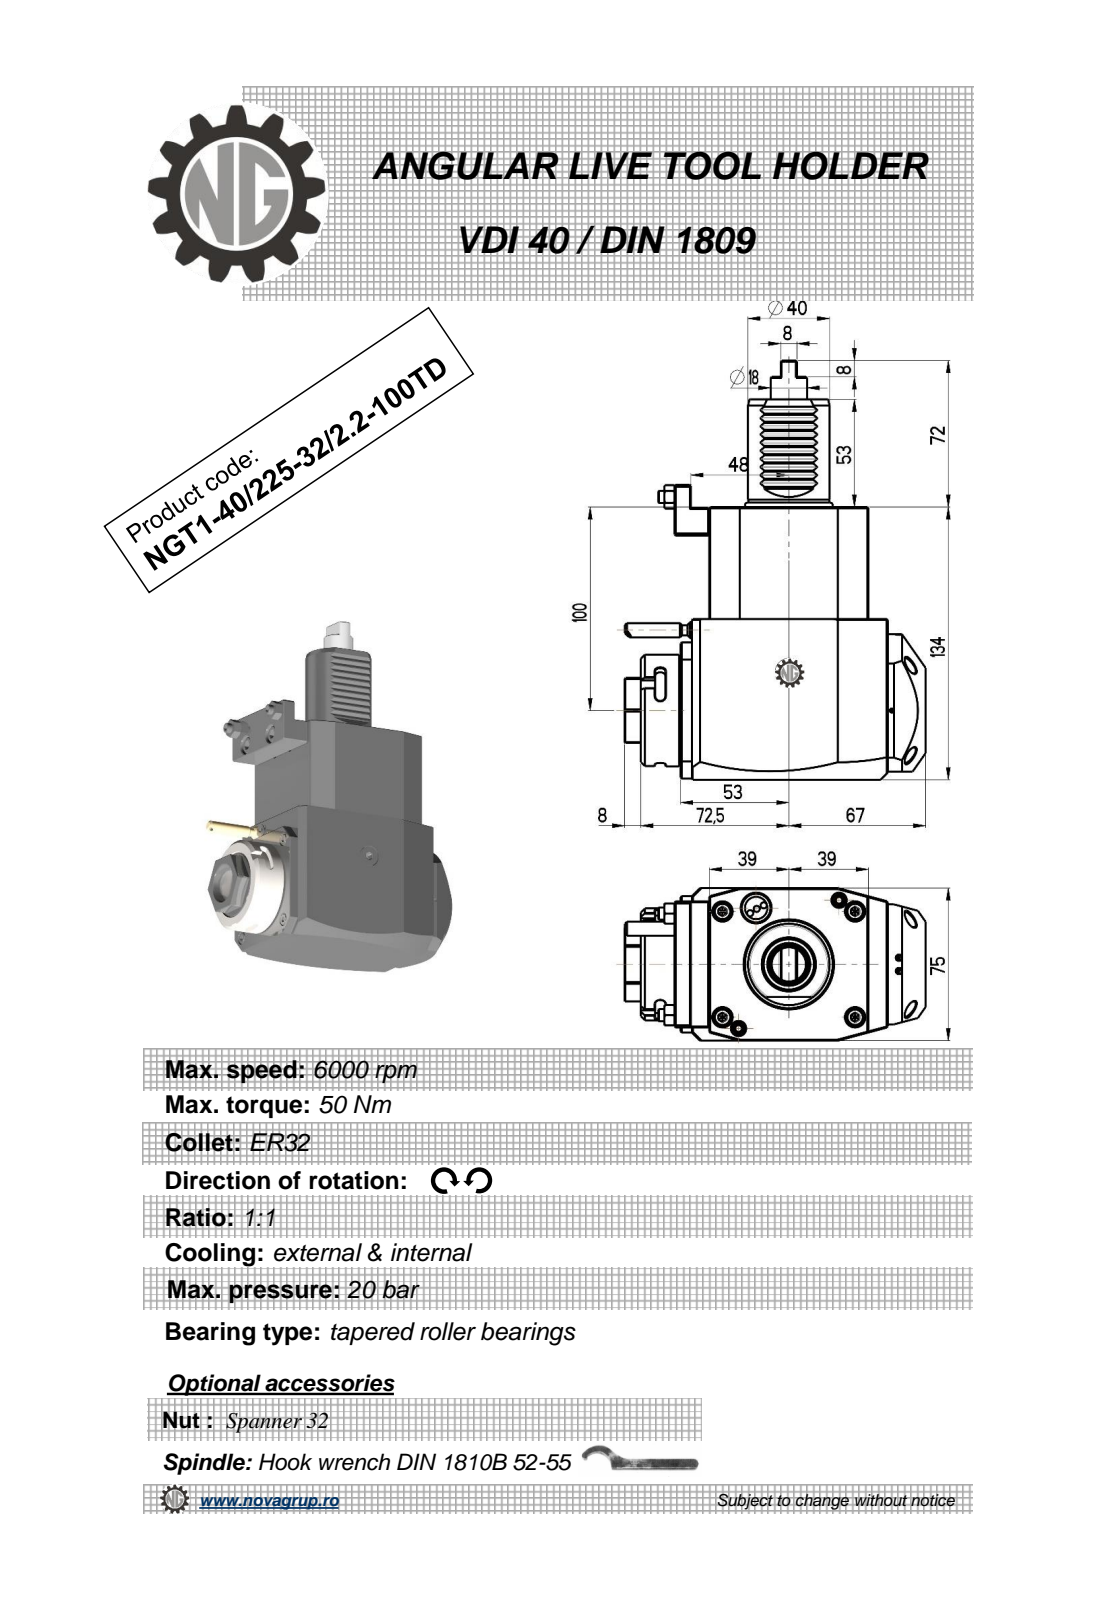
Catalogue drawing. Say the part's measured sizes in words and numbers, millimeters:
The part is named "NGT1_40_225_32_1_2_100TD". Its 3-D file was written by "PRO/ENGINEER BY PARAMETRIC TECHNOLOGY CORPORATION, 2010280 (CONFIG_CONTROL_DESIGN)". It is 1 solid with 332 faces: 184 planar, 62 cylindrical and 86 other. Overall it measures 206 by 147.5 by 75 millimeters. Its volume is 1 081 000 cubic millimeters and its surface area 78 356 square millimeters. Round holes: 1 of diameter 2.5, 1 of diameter 3, 1 of diameter 23. Round bosses or shafts: 2 of diameter 6, 1 of diameter 55, 1 of diameter 48, 1 of diameter 40, 1 of diameter 17.8, 1 of diameter 8, 1 of diameter 7, 1 of diameter 5. Partial cylindrical surfaces (rounded edges, fillets, slot ends): 10 of radius 0.3, 10 of radius 0.31, 6 of radius 2.5, 2 of radius 0.8, 2 of radius 180, 1 of radius 0.5, 1 of radius 24.5, 1 of radius 37.5. The main face-to-face distances are 75, 134, 14, 78, 92, 120, 0.5, 8.5, 19.5, 84.88. The hole center spacings are 43.2.
